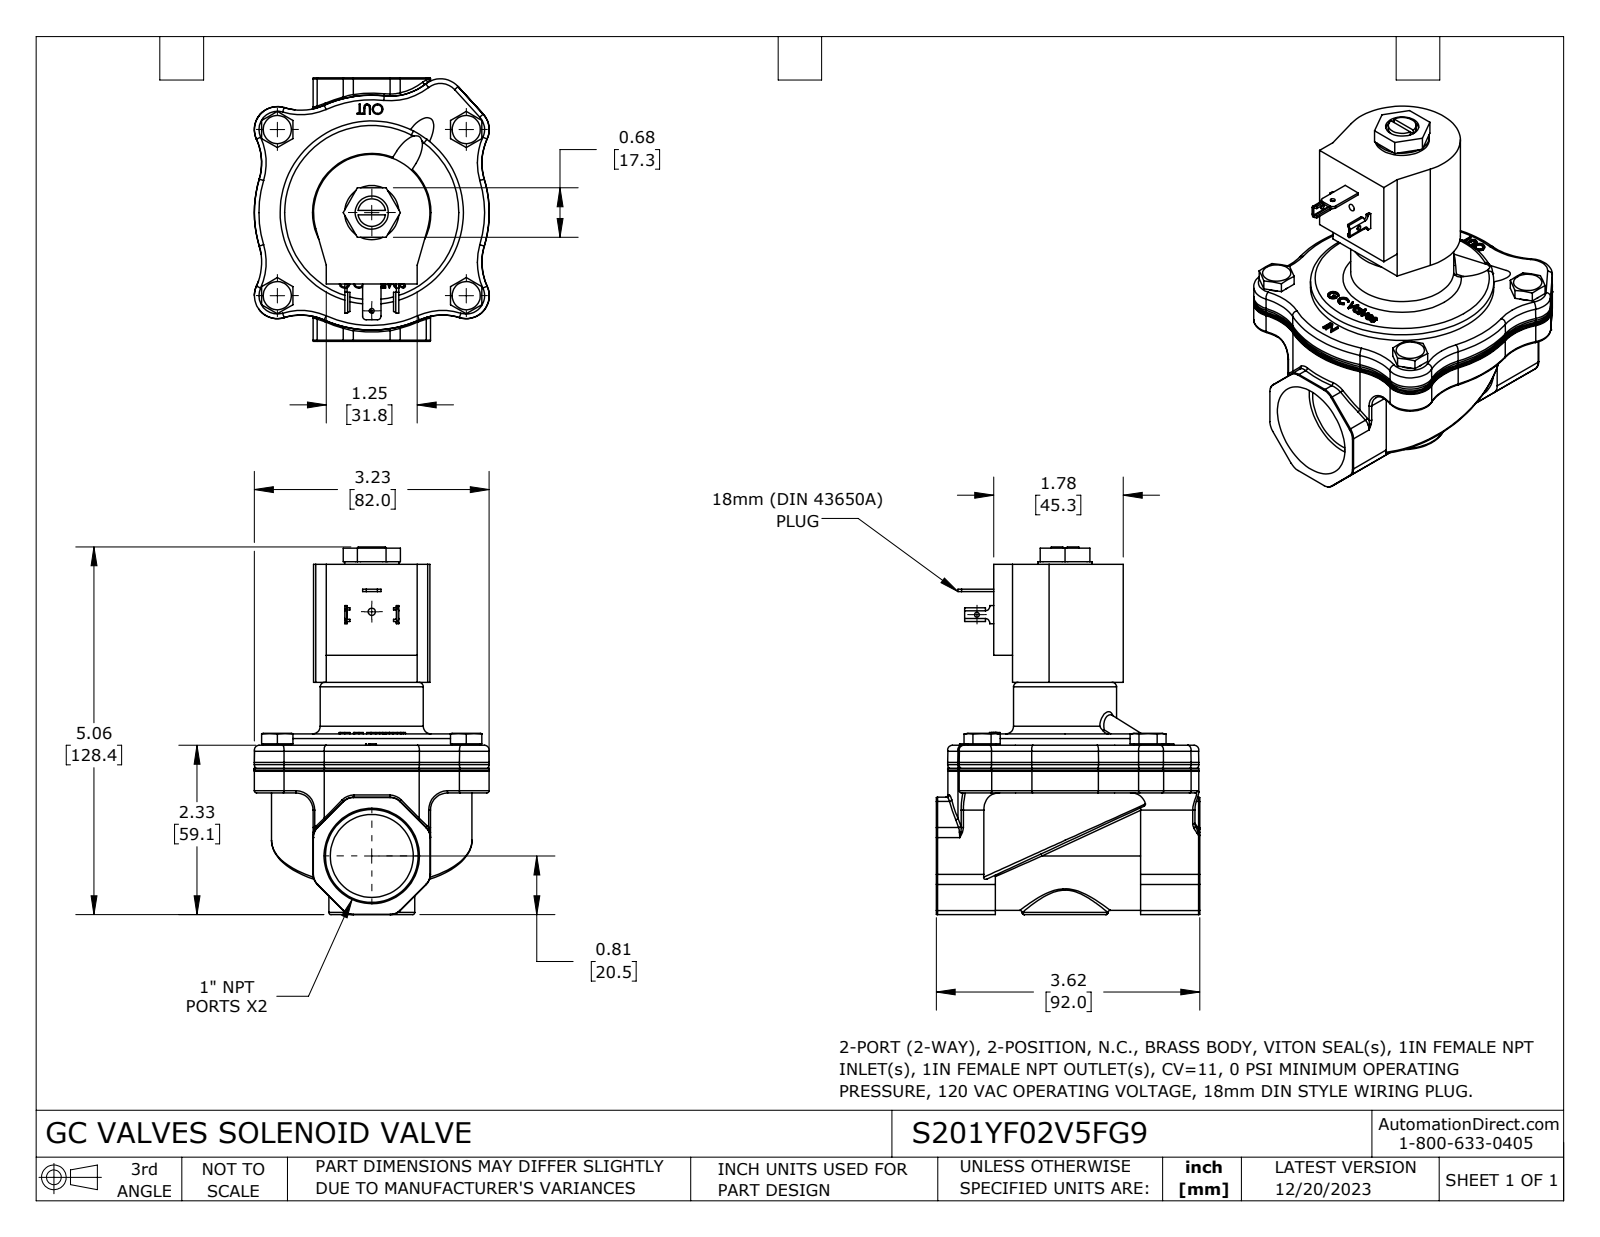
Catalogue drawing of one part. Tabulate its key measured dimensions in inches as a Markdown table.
| quantity | value |
| --- | --- |
| part name | S201YF02V5FG9 |
| STEP written by | SolidWorks 2023 (CONFIG_CONTROL_DESIGN) |
| units | inches |
| bodies | 1 solid, 671 faces (220 planar, 172 cylindrical, 279 other) |
| overall size | 5.055 × 3.622 × 3.232 |
| volume | 19.13 in³ |
| surface area | 70.49 in² |
| round holes (diameter × count) | 0.066 × 1, 0.067 × 1, 0.1 × 1, 0.456 × 1, 1.141 × 1 |
| round bosses / shafts (diameter × count) | 0.388 × 4, 2.52 × 1, 1.417 × 1, 1.181 × 1, 0.746 × 1, 0.38 × 1 |
| partial cylindrical surfaces (radius × count) | 0.031 × 24, 0.787 × 24, 0.315 × 12, 0.197 × 8, 0.006 × 4, 0.041 × 4, 0.05 × 2, 0.06 × 2 |
| main face-to-face distances | 0.157, 0.655, 0.812, 3.141, 2.486, 2.329, 2.485, 2.328, 1.673, 4.814 |
| hole center spacings | 1.35, 3.356 |
